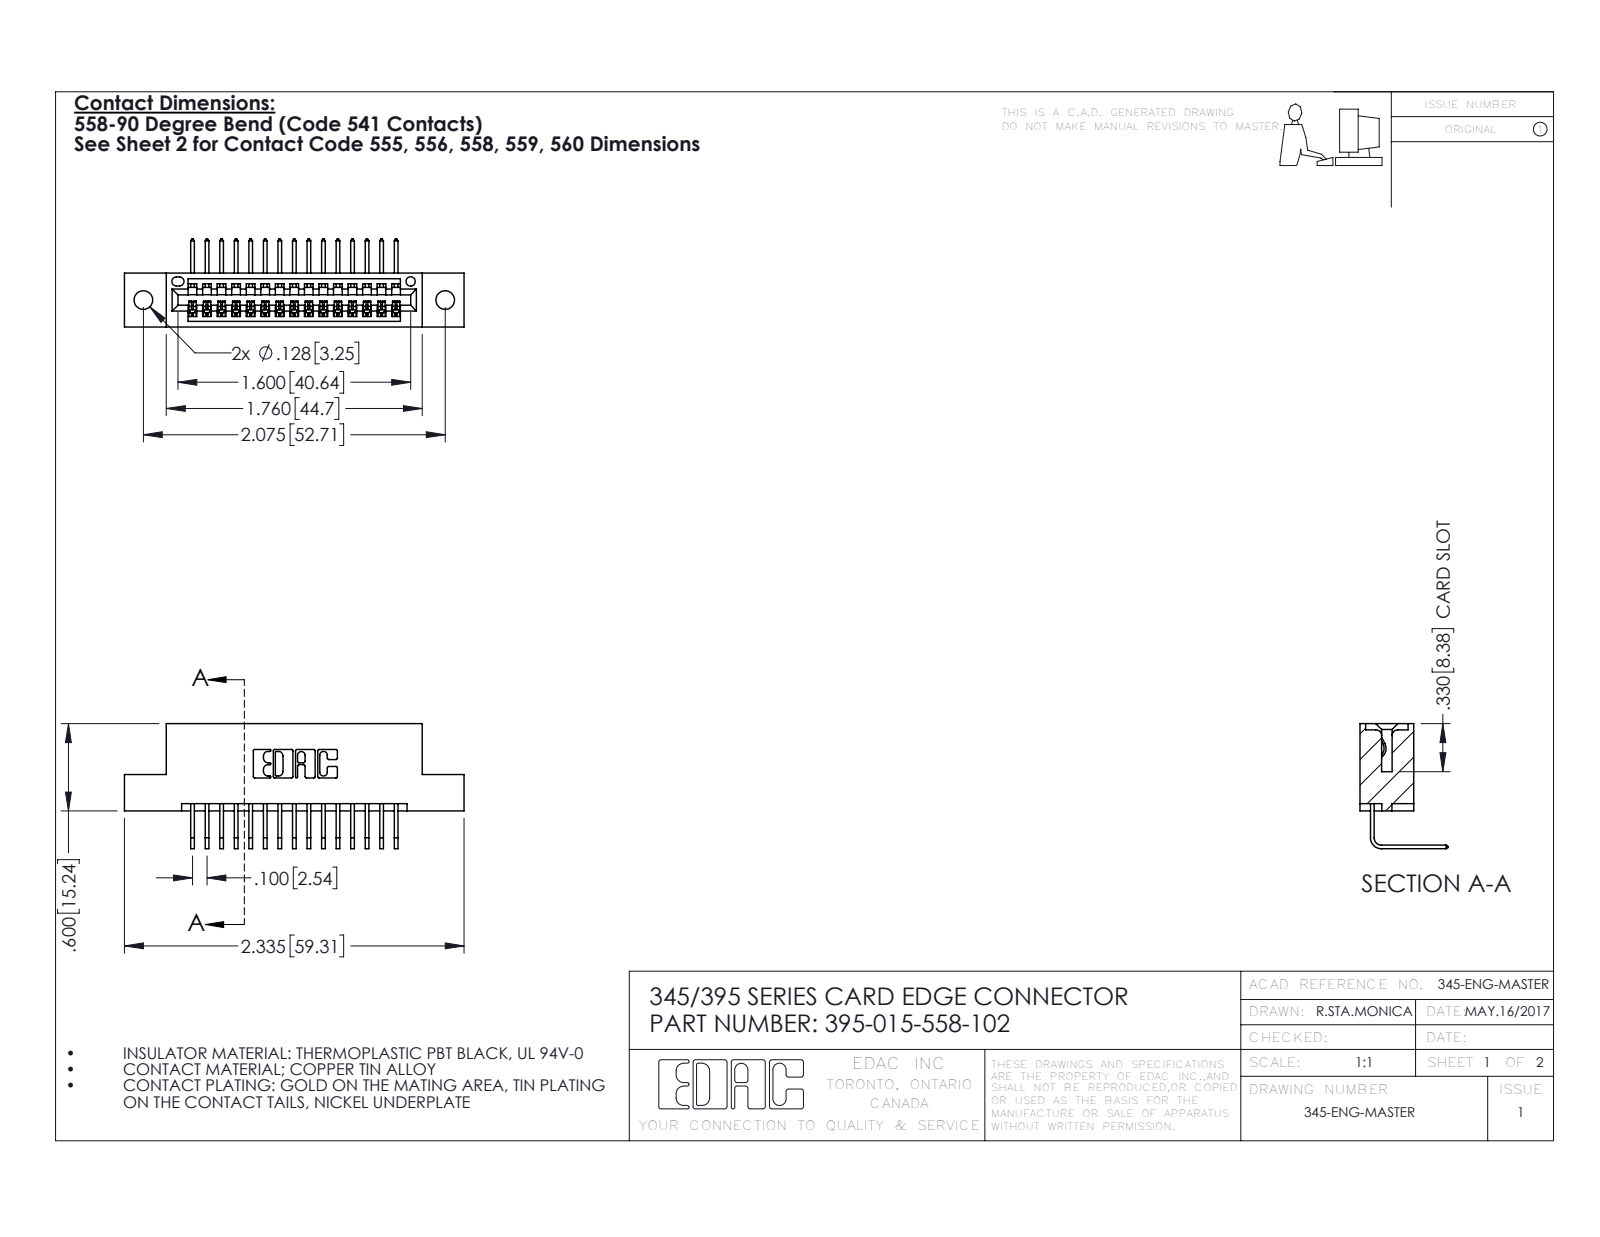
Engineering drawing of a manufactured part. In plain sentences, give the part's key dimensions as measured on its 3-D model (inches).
The part is named "345 Part_Flush Mounting Lugs - 0.128 Dia; 345-292-001_558 Tail - 2; 395-015-558-102". Its 3-D file was written by "SolidWorks 2016 (CONFIG_CONTROL_DESIGN)". It is 16 solids with 1026 faces: 710 planar, 316 cylindrical and 0 other. Overall it measures 2.335 by 0.859 by 0.605 inches. Its volume is 0.331 cubic inches and its surface area 10.64 square inches. Round holes: 2 of diameter 0.128, 1 of diameter 0.064. Partial cylindrical surfaces (rounded edges, fillets, slot ends): 30 of radius 0.006, 22 of radius 0.01, 6 of radius 0.007, 6 of radius 0.031, 3 of radius 0.026, 2 of radius 0.031, 2 of radius 0.04, 1 of radius 0.014. The main face-to-face distances are 0.2, 0.298, 0.072, 0.37, 0.098, 0.272, 0.025, 0.1, 0.225, 0.05. The hole center spacings are 0.27, 1.842, 2.075.
